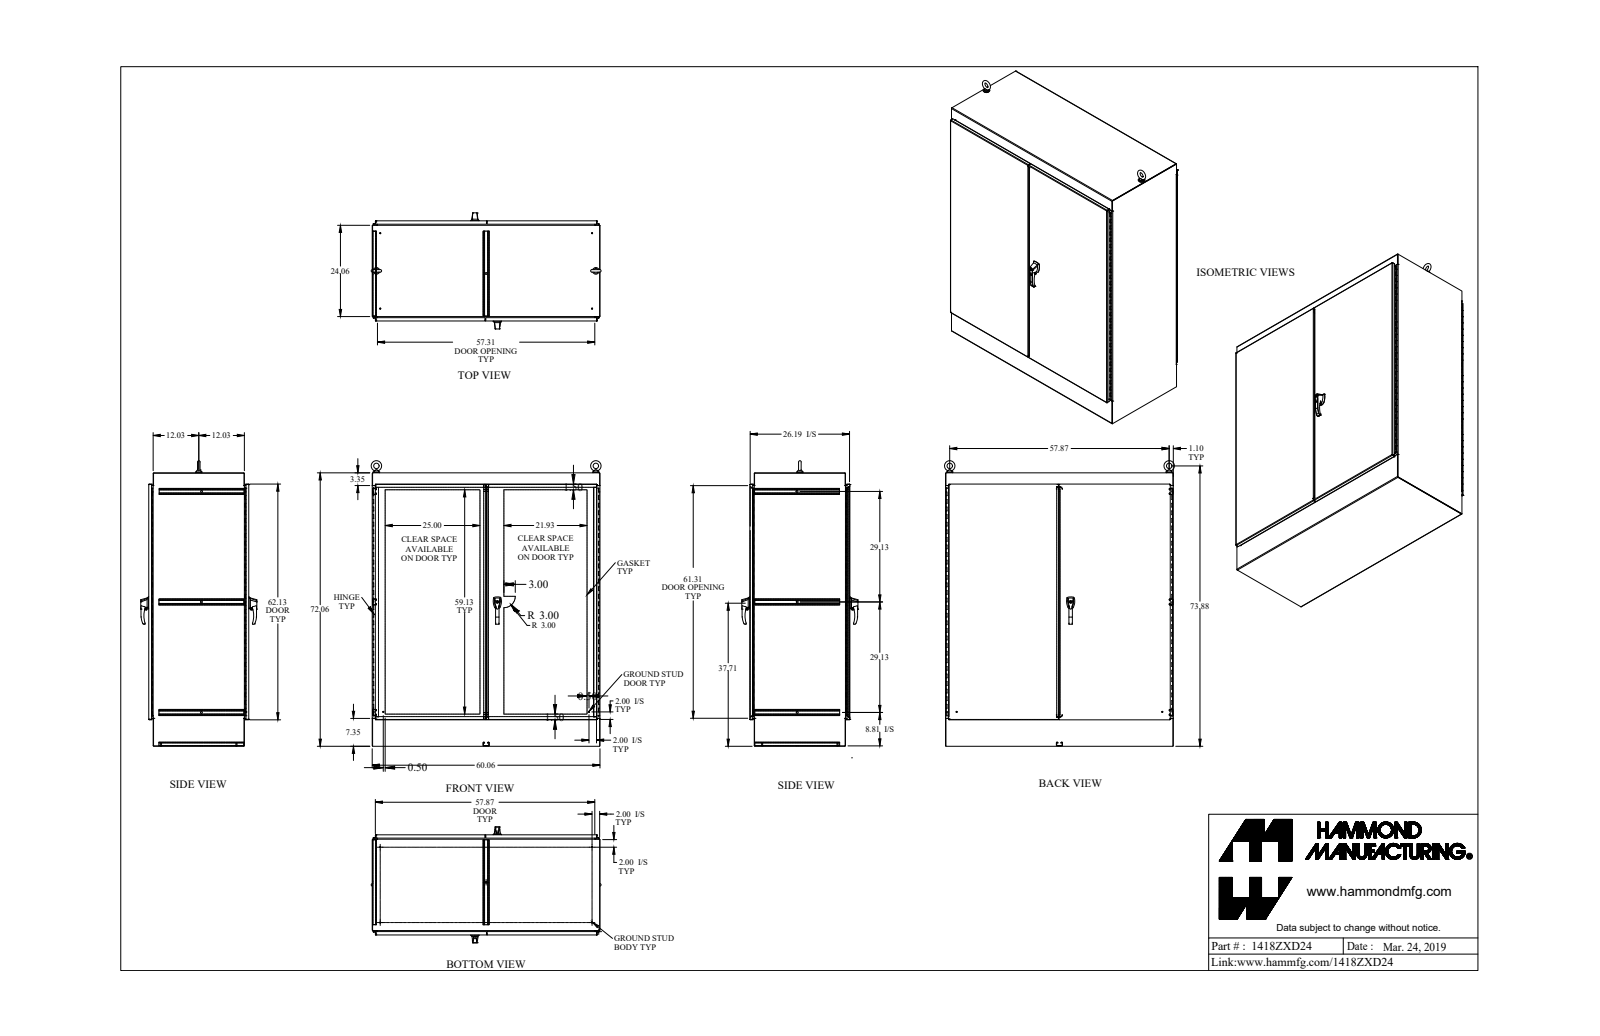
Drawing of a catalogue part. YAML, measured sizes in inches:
part_name: "1418ZXD24_Default"
step_written_by: "SolidWorks 2019 (CONFIG_CONTROL_DESIGN)"
units: inches
bodies: {solids: 109, faces: 4534, planar: 2056, cylindrical: 2212, other: 266}
overall_size: [75.713, 61.119, 30.614]
volume: 1829
surface_area: 37843
round_holes:
  - {diameter: 0.304, count: 40}
  - {diameter: 0.5, count: 5}
  - {diameter: 0.11, count: 4}
  - {diameter: 0.25, count: 4}
  - {diameter: 0.257, count: 4}
  - {diameter: 0.28, count: 4}
  - {diameter: 0.281, count: 4}
  - {diameter: 0.313, count: 4}
  - {diameter: 0.39, count: 4}
  - {diameter: 0.413, count: 4}
  - {diameter: 0.173, count: 2}
  - {diameter: 0.233, count: 2}
round_bosses_or_shafts:
  - {diameter: 0.281, count: 12}
  - {diameter: 0.25, count: 8}
  - {diameter: 1, count: 4}
  - {diameter: 0.75, count: 4}
  - {diameter: 0.63, count: 4}
  - {diameter: 0.625, count: 4}
  - {diameter: 0.44, count: 4}
  - {diameter: 0.37, count: 4}
partial_cylinders:
  - {radius: 0.043, count: 54}
  - {radius: 0.138, count: 48}
  - {radius: 0.125, count: 44}
  - {radius: 0.048, count: 40}
  - {radius: 0.143, count: 40}
  - {radius: 0.018, count: 32}
  - {radius: 0.05, count: 16}
  - {radius: 0.06, count: 16}
face_to_face_distances: [0.095, 0.095, 26.289, 26.194, 26.384, 59.965, 71.965, 59.87, 60.06, 1.162]
hole_center_spacings: [6, 12, 18, 58.637, 24, 59.55, 30, 61.043]
